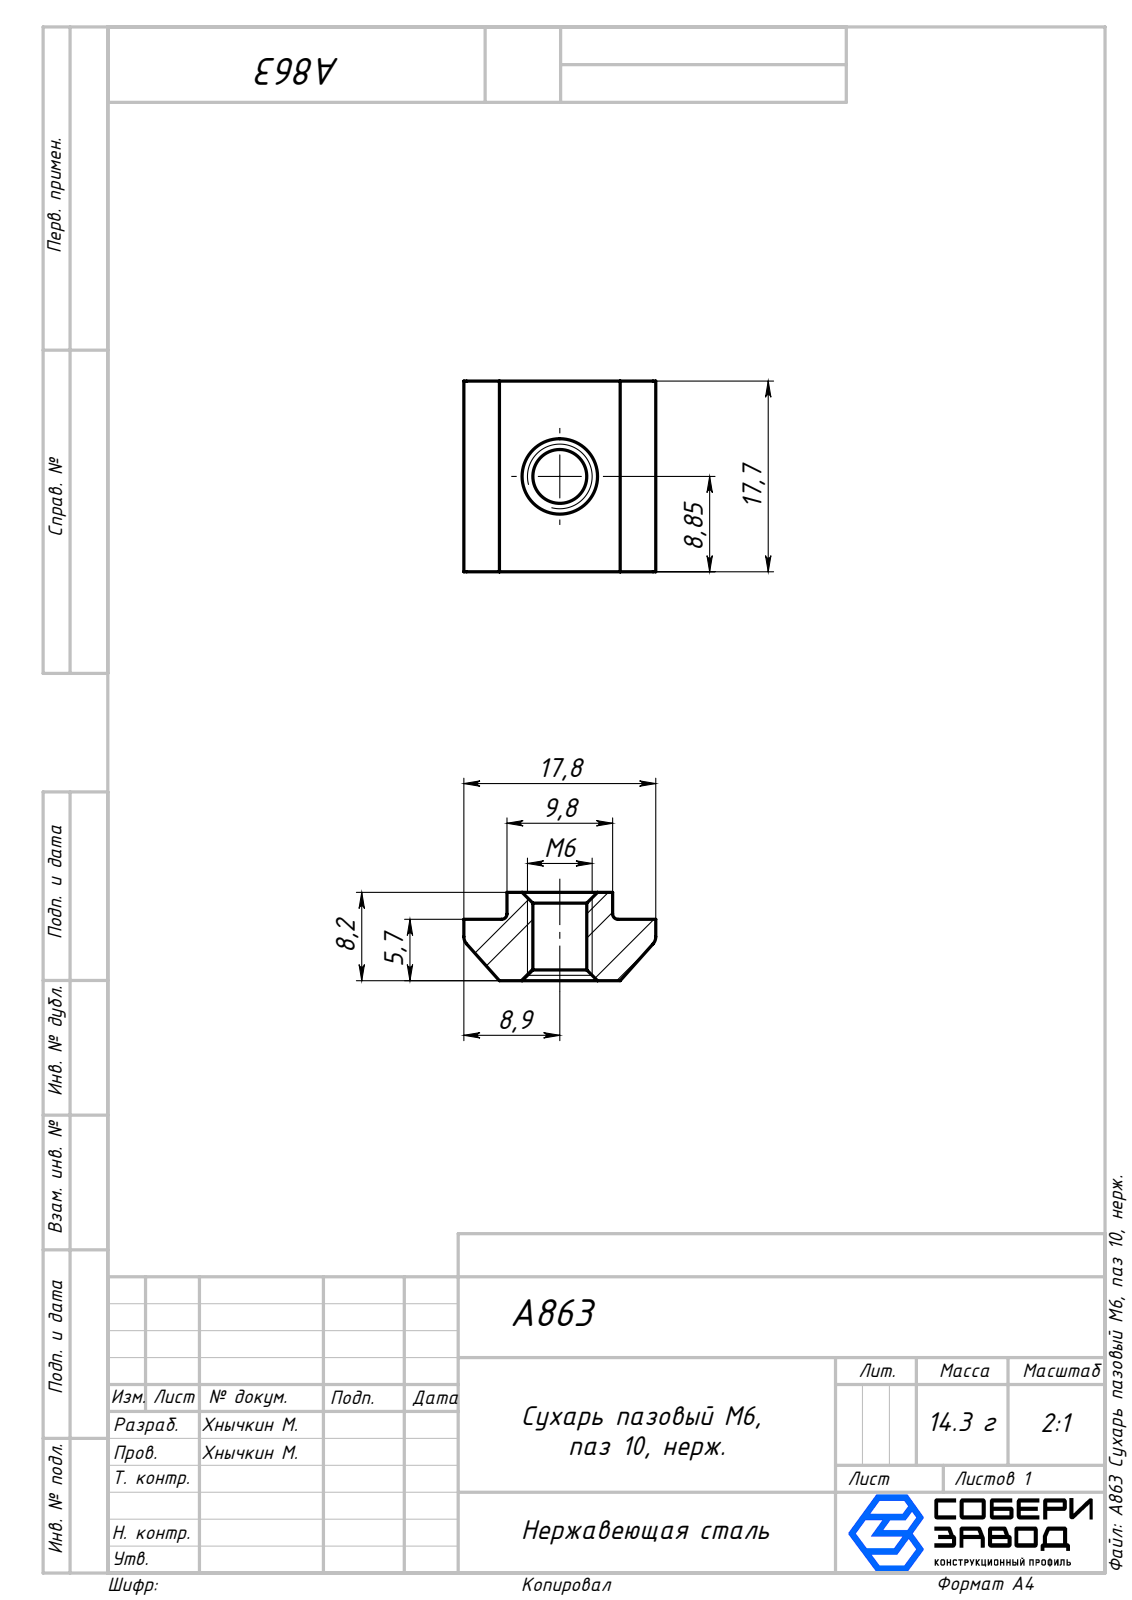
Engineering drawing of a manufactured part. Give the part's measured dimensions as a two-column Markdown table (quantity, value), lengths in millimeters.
| quantity | value |
| --- | --- |
| part name | A863 Сухарь пазовый М6, паз 10, нерж. |
| STEP written by | SolidWorks 2025 (AUTOMOTIVE_DESIGN) |
| units | millimeters |
| bodies | 1 solid, 22 faces (12 planar, 6 cylindrical, 4 other) |
| overall size | 17.8 × 17.7 × 8.2 |
| volume | 1 836 mm³ |
| surface area | 1 141 mm² |
| round holes (diameter × count) | 5 × 1 |
| partial cylindrical surfaces (radius × count) | 0.5 × 2, 1 × 2 |
| main face-to-face distances | 8.2, 5.7, 2.5, 17.7, 4, 13.8, 9.8, 17.8 |
